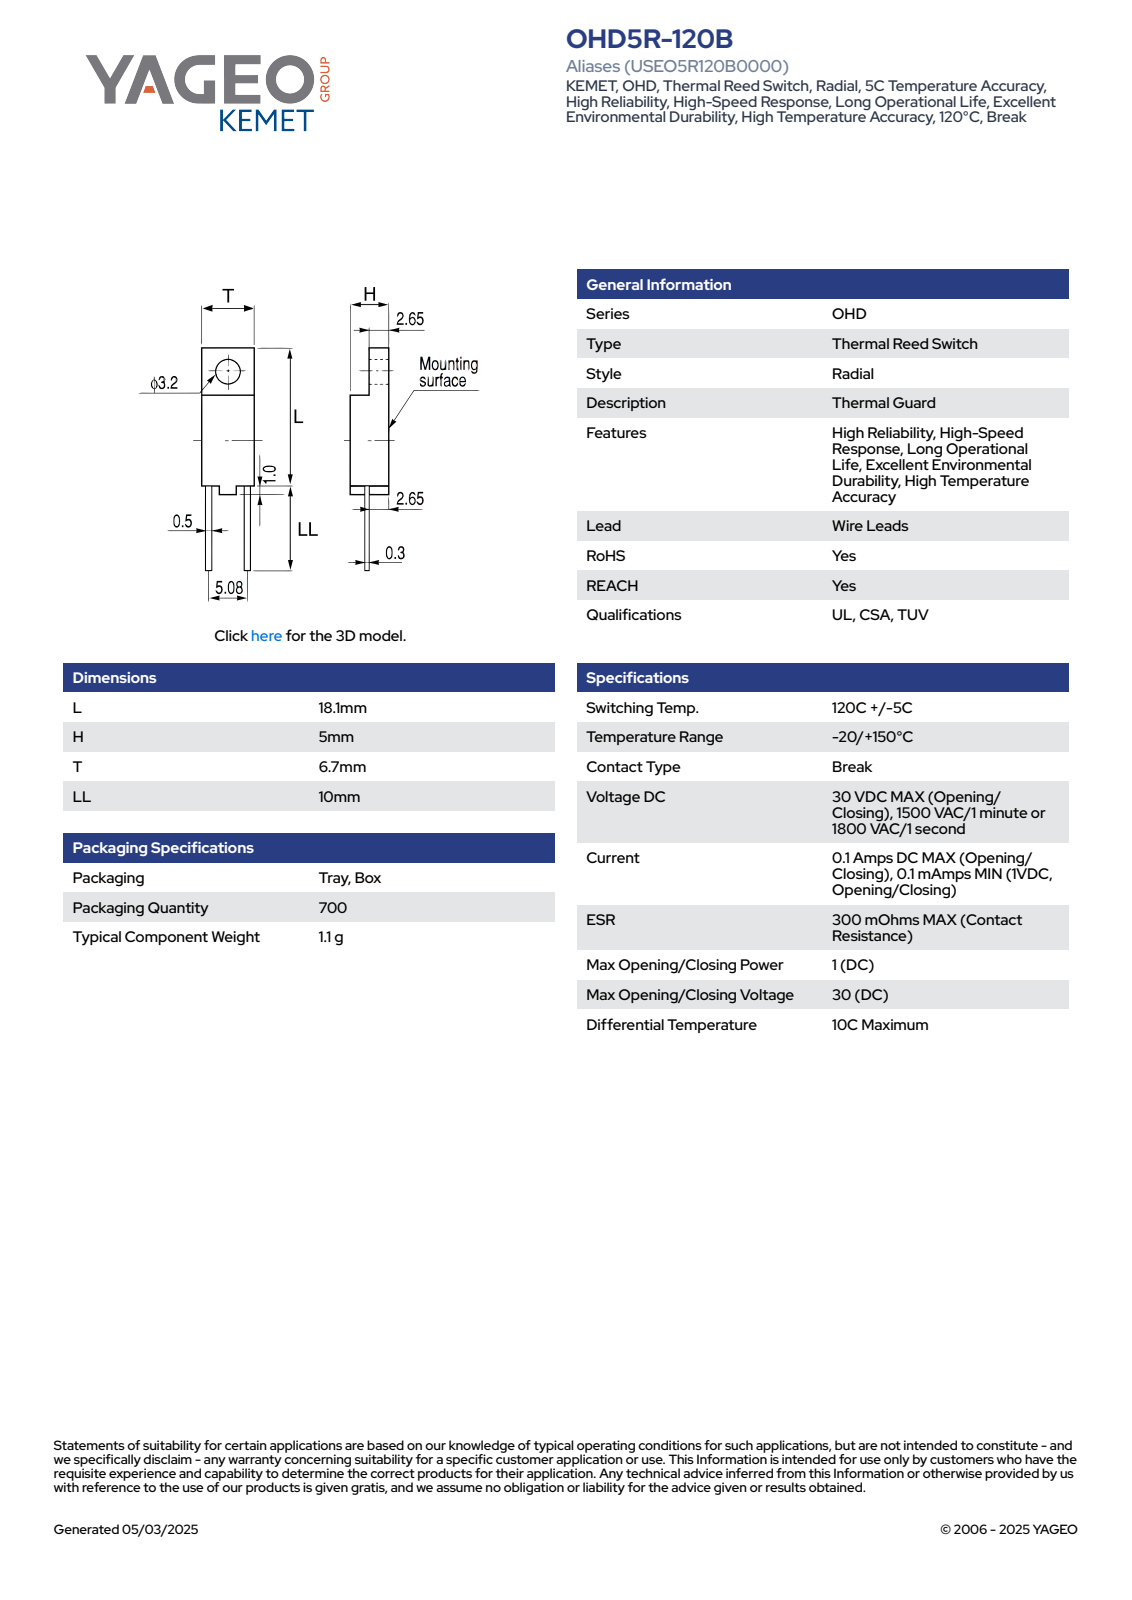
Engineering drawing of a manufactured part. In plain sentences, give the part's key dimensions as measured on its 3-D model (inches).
The part is named "Default". Its 3-D file was written by "SolidWorks 2014 (AUTOMOTIVE_DESIGN)". It is 1 solid with 106 faces: 76 planar, 22 cylindrical and 8 other. Overall it measures 1.106 by 0.264 by 0.197 inches. Its volume is 0.031 cubic inches and its surface area 0.795 square inches. Round holes: 1 of diameter 0.126. Partial cylindrical surfaces (rounded edges, fillets, slot ends): 14 of radius 0.004, 4 of radius 0.016. The main face-to-face distances are 0.197, 0.264, 0.104, 0.093, 0.495, 0.713, 0.217, 0.116, 0.081, 0.159.
